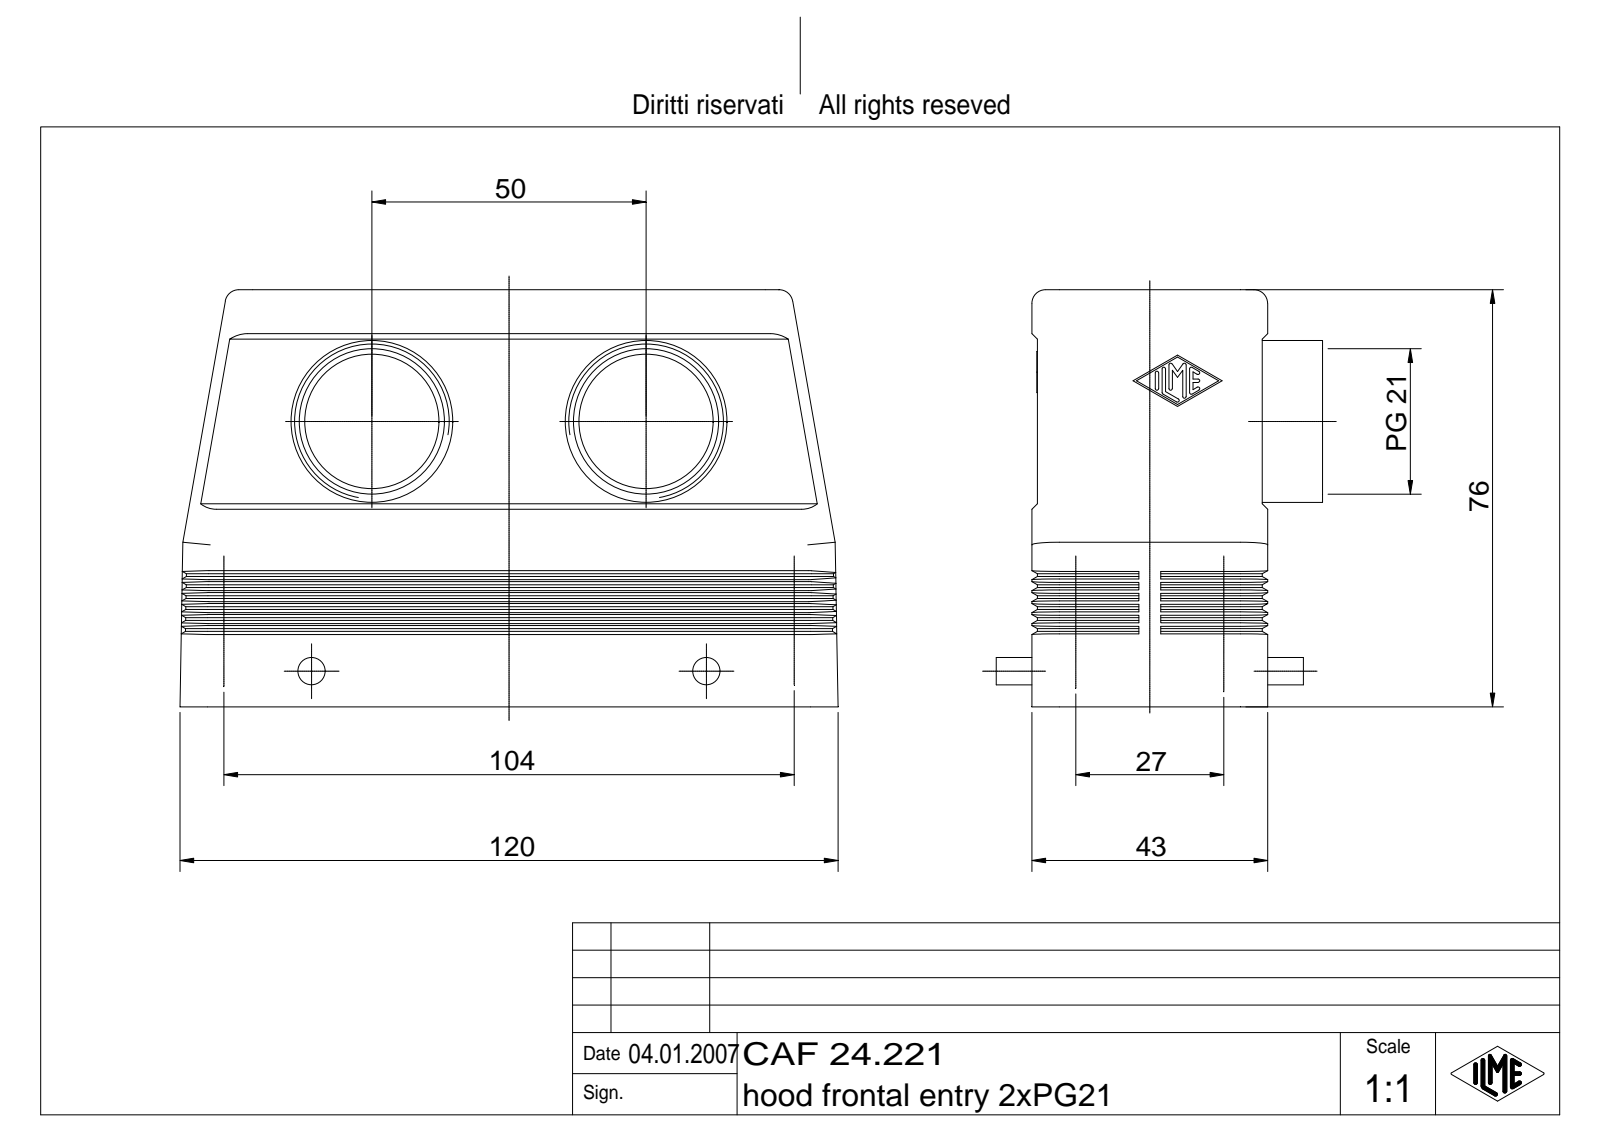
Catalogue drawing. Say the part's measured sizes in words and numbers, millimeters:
The part is named "CAF 24.221". Its 3-D file was written by "Autodesk Inventor 7 (AUTOMOTIVE_DESIGN)". It is 1 solid with 456 faces: 150 planar, 136 cylindrical and 170 other. Overall it measures 120 by 76 by 59.5 millimeters. Its volume is 81 560 cubic millimeters and its surface area 58 663 square millimeters. Round holes: 2 of diameter 24.5, 1 of diameter 26.5, 1 of diameter 28. Round bosses or shafts: 2 of diameter 5, 1 of diameter 29.5. Partial cylindrical surfaces (rounded edges, fillets, slot ends): 14 of radius 0.25, 12 of radius 4, 8 of radius 2, 8 of radius 5, 4 of radius 2.5, 4 of radius 3.5. The main face-to-face distances are 3, 40, 37, 2, 39, 42, 1, 43, 41, 1.73. The hole center spacings are 50.
